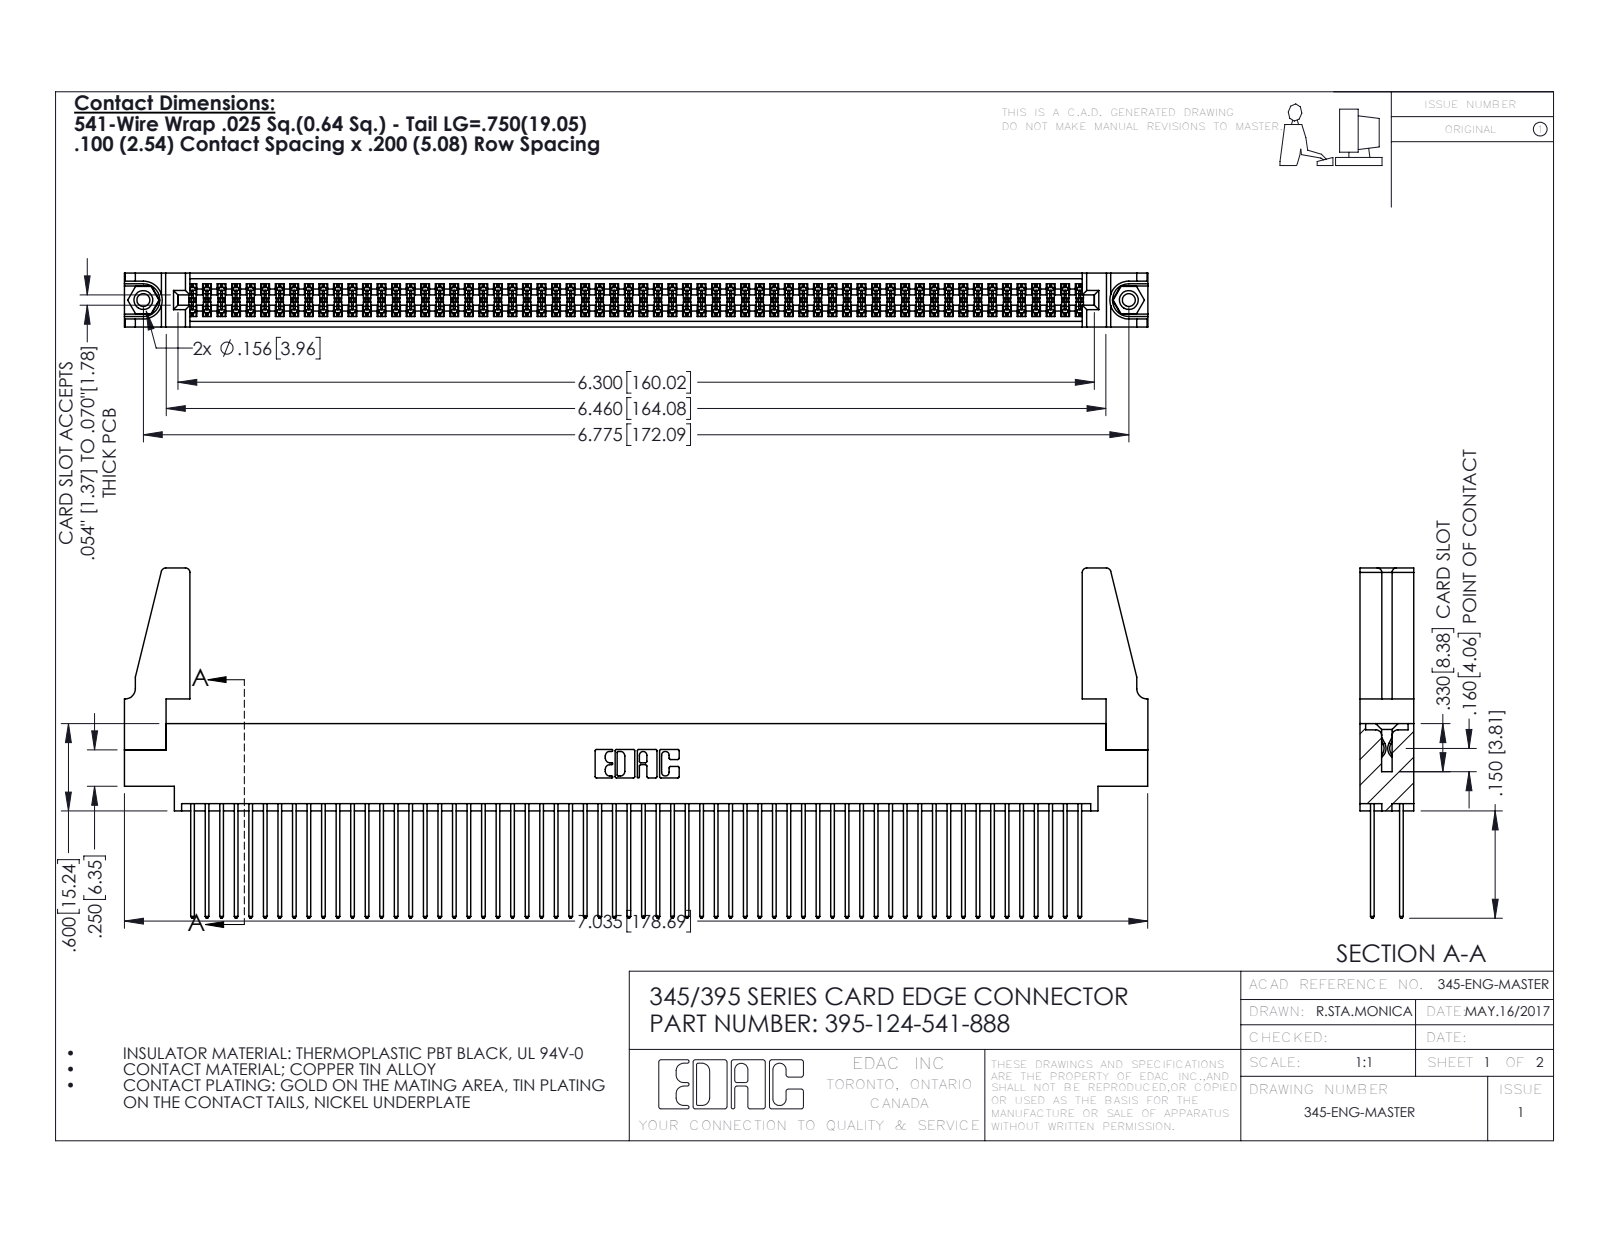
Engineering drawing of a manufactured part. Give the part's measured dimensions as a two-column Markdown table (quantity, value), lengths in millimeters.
| quantity | value |
| --- | --- |
| part name | 345-250-001_345-250-001-102; 345-292-001_345-293-141; 395-124-541-888; 345 Part_0.170 Offset - 0.156 Dia-TH (+1 more) |
| STEP written by | SolidWorks 2016 (CONFIG_CONTROL_DESIGN) |
| units | millimeters |
| bodies | 129 solids, 6454 faces (4248 planar, 2190 cylindrical, 16 other) |
| overall size | 178.7 × 61.1 × 9.4 |
| volume | 21 400 mm³ |
| surface area | 33 820 mm² |
| round holes (diameter × count) | 2.3 × 2, 3.2 × 2, 4 × 2, 1.6 × 1 |
| round bosses / shafts (diameter × count) | 3.9 × 2 |
| partial cylindrical surfaces (radius × count) | 0.2 × 186, 0.3 × 124, 0.3 × 22, 0.8 × 8, 0.2 × 6, 0.8 × 6, 0.7 × 3, 0.4 × 2 |
| main face-to-face distances | 1.8, 7.6, 2.5, 6.9, 0.6, 5.1, 9.4, 5.7, 4.4, 3.8 |
| hole center spacings | 6.9, 166.1, 172.1 |
